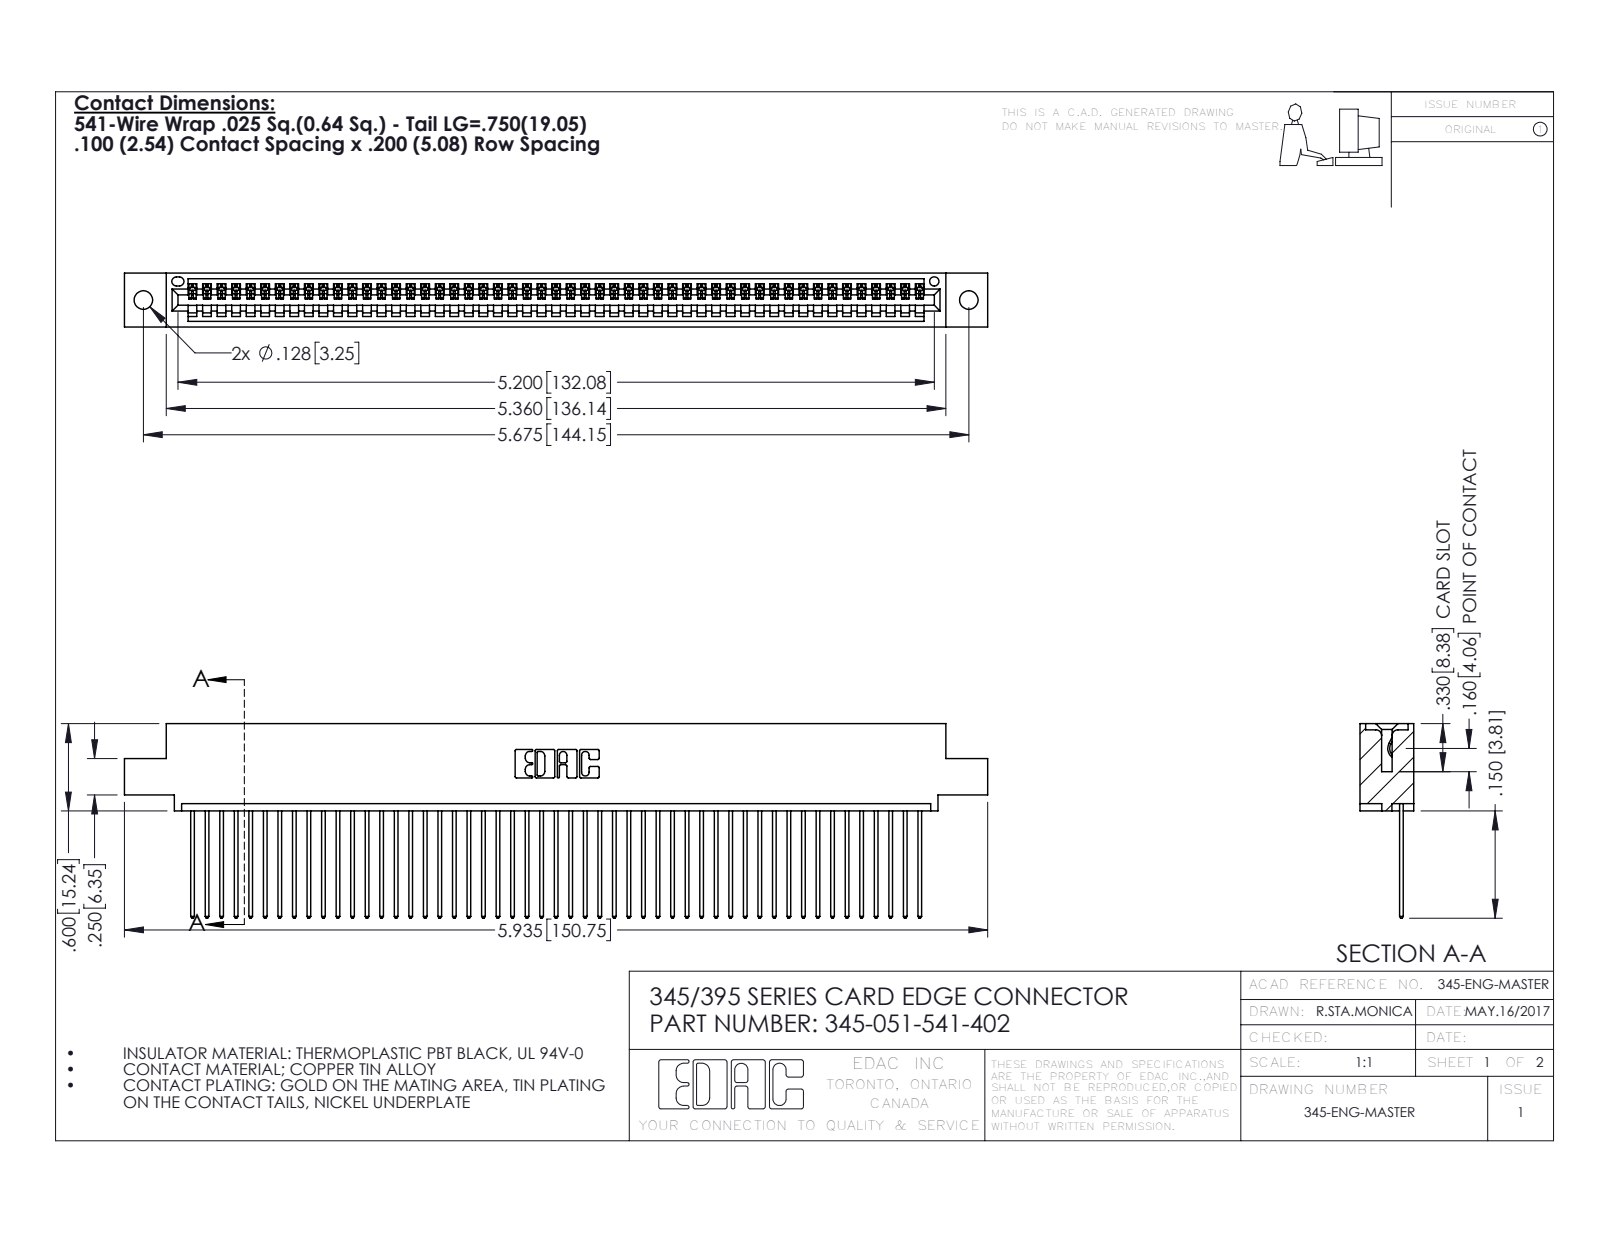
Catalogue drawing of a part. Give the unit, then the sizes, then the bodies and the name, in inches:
Units: inches
Overall size (bounding box): 5.935 × 1.337 × 0.37
Round holes (diameter × count): ⌀0.128 ×2, ⌀0.064 ×1
Partial cylindrical surfaces — rounded edges, fillets, slot ends (radius × count): R0.006 ×102, R0.01 ×102, R0.01 ×22, R0.007 ×6, R0.031 ×6, R0.026 ×3, R0.031 ×2, R0.04 ×2
Main face-to-face distances: 0.072, 0.298, 0.098, 0.272, 0.025, 0.37, 0.2, 0.225, 0.149, 0.072
Hole centre spacings: 0.27, 5.439, 5.675
Volume: 0.882 in³ · Surface area: 31.2 in²
Bodies: 52 solids, 3088 faces (2124 planar, 964 cylindrical, 0 other)
Part name (STEP PRODUCT): 345-292-001_345-293-141; 345 Part_0.110 Offset - 0.128 Dia; 345-051-541-402
STEP written by: SolidWorks 2016 (CONFIG_CONTROL_DESIGN)
